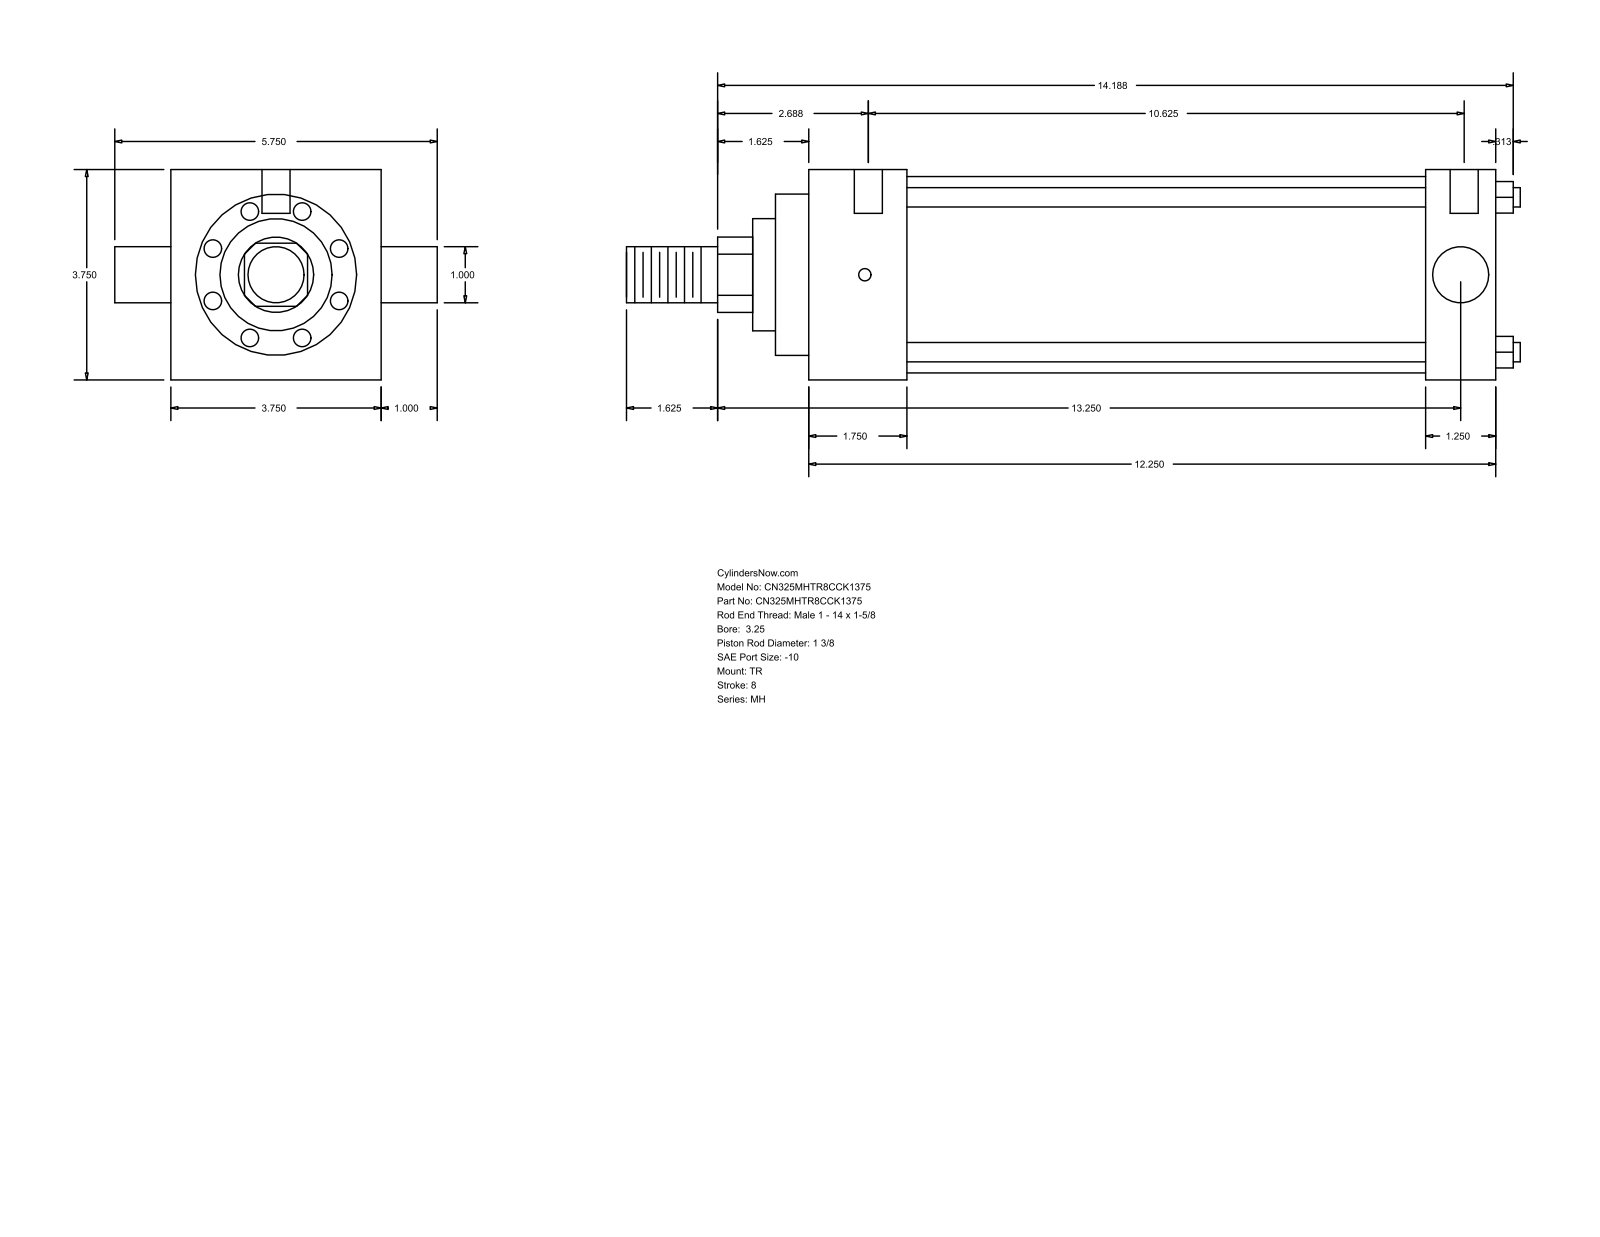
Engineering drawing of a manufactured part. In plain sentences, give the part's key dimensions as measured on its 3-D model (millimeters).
The part is named "MH_TR__0325_1.375". Its 3-D file was written by "GSSL Pune (CONFIG_CONTROL_DESIGN)". It is 0 solids with 86 faces: 61 planar, 25 cylindrical and 0 other. Overall it measures 404.81 by 146.05 by 95.25 millimeters. Round holes: 3 of diameter 5.56, 2 of diameter 12.7. Round bosses or shafts: 4 of diameter 8.76, 2 of diameter 25.4, 1 of diameter 88.9, 1 of diameter 73.03, 1 of diameter 50.8, 1 of diameter 34.92. Partial cylindrical surfaces (rounded edges, fillets, slot ends): 1 of radius 17.06. The main face-to-face distances are 95.24, 311.16, 44.45, 279.41, 234.96, 266.71, 31.75, 15.08, 59.53, 294.49. The hole center spacings are 1.59, 4.76, 269.88, 271.47, 274.64, 276.23.
